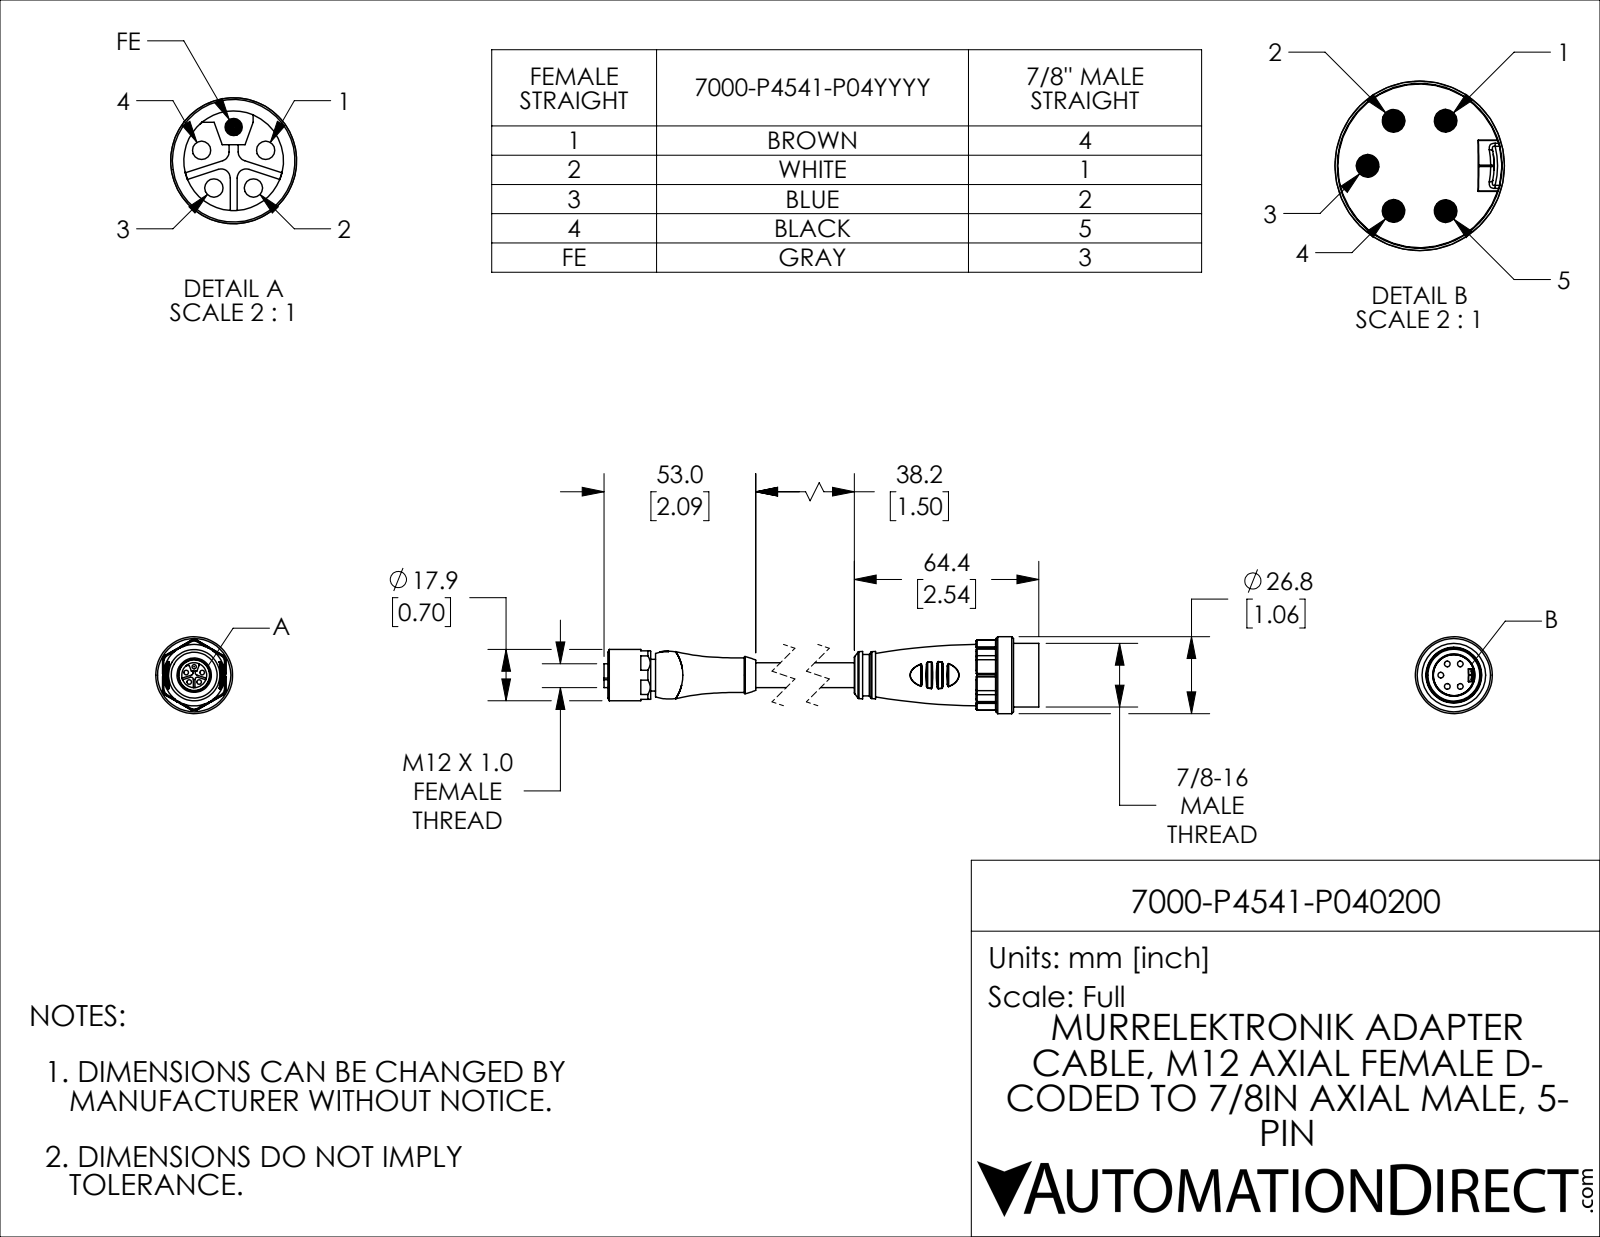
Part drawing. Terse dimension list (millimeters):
name: 7000-P4541-P040200; 7000-P4541-P040200_2; 7000-P4541-P040200_1
written by: SolidWorks 2021 (CONFIG_CONTROL_DESIGN)
unit: mm
bodies: 3 solids, 396 faces (105 planar, 120 cylindrical, 171 other)
size: 155.6 × 26.8 × 26.8
volume: 31 230 mm³; area: 11 370 mm²
holes: 4× ⌀1.6, 1× ⌀11, 1× ⌀13, 1× ⌀18.8
bosses: 5× ⌀2, 1× ⌀26.8, 1× ⌀22.2, 1× ⌀18.7, 1× ⌀17.9, 1× ⌀14.5, 1× ⌀13, 1× ⌀11.1
rounds: 18× R0.2, 18× R0.5, 4× R0.8, 3× R0.3, 2× R2.2, 2× R36, 1× R12.2
face distances: 22, 4.5, 15, 6.1, 10.6, 122.6, 128.8, 133.3, 137.6, 15
hole spacings: 2.9, 3.5, 5.6
